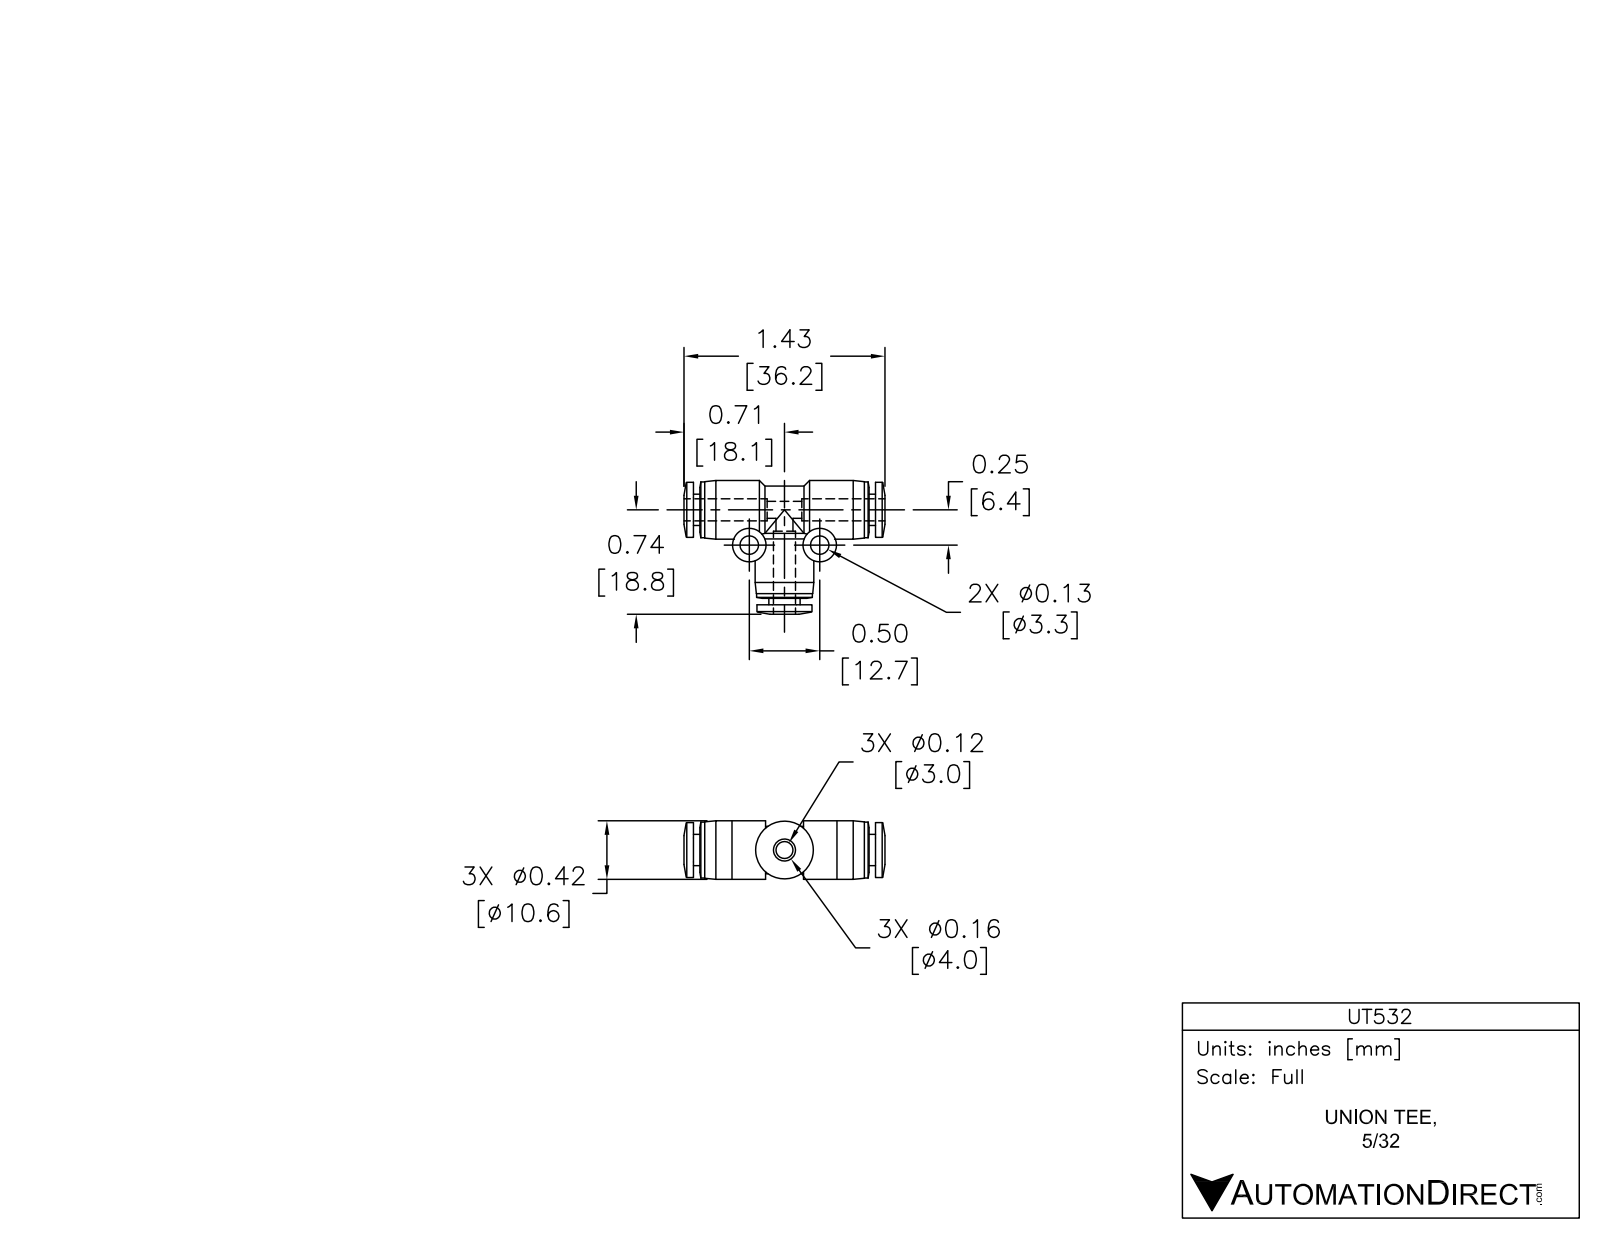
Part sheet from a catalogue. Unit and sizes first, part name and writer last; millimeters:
Units: millimetres
Overall size (bounding box): 36 × 24 × 10.5
Round holes (diameter × count): ⌀3.3 ×2, ⌀3.4 ×2, ⌀4.2 ×2
Round bosses / shafts (diameter × count): ⌀10.5 ×2, ⌀10 ×2, ⌀9.7 ×2, ⌀6 ×2, ⌀5.6 ×2, ⌀8.5 ×1
Partial cylindrical surfaces — rounded edges, fillets, slot ends (radius × count): R4.2 ×1
Main face-to-face distances: 1.1, 31.4, 32.6, 10.5, 30.3, 13.1, 11.9, 19.5, 18.3, 1.7
Hole centre spacings: 12.8
Volume: 3 380 mm³ · Surface area: 3 074 mm²
Bodies: 1 solid, 97 faces (19 planar, 46 cylindrical, 32 other)
Part name (STEP PRODUCT): UT532
STEP written by: SolidWorks 2015 (AUTOMOTIVE_DESIGN)
